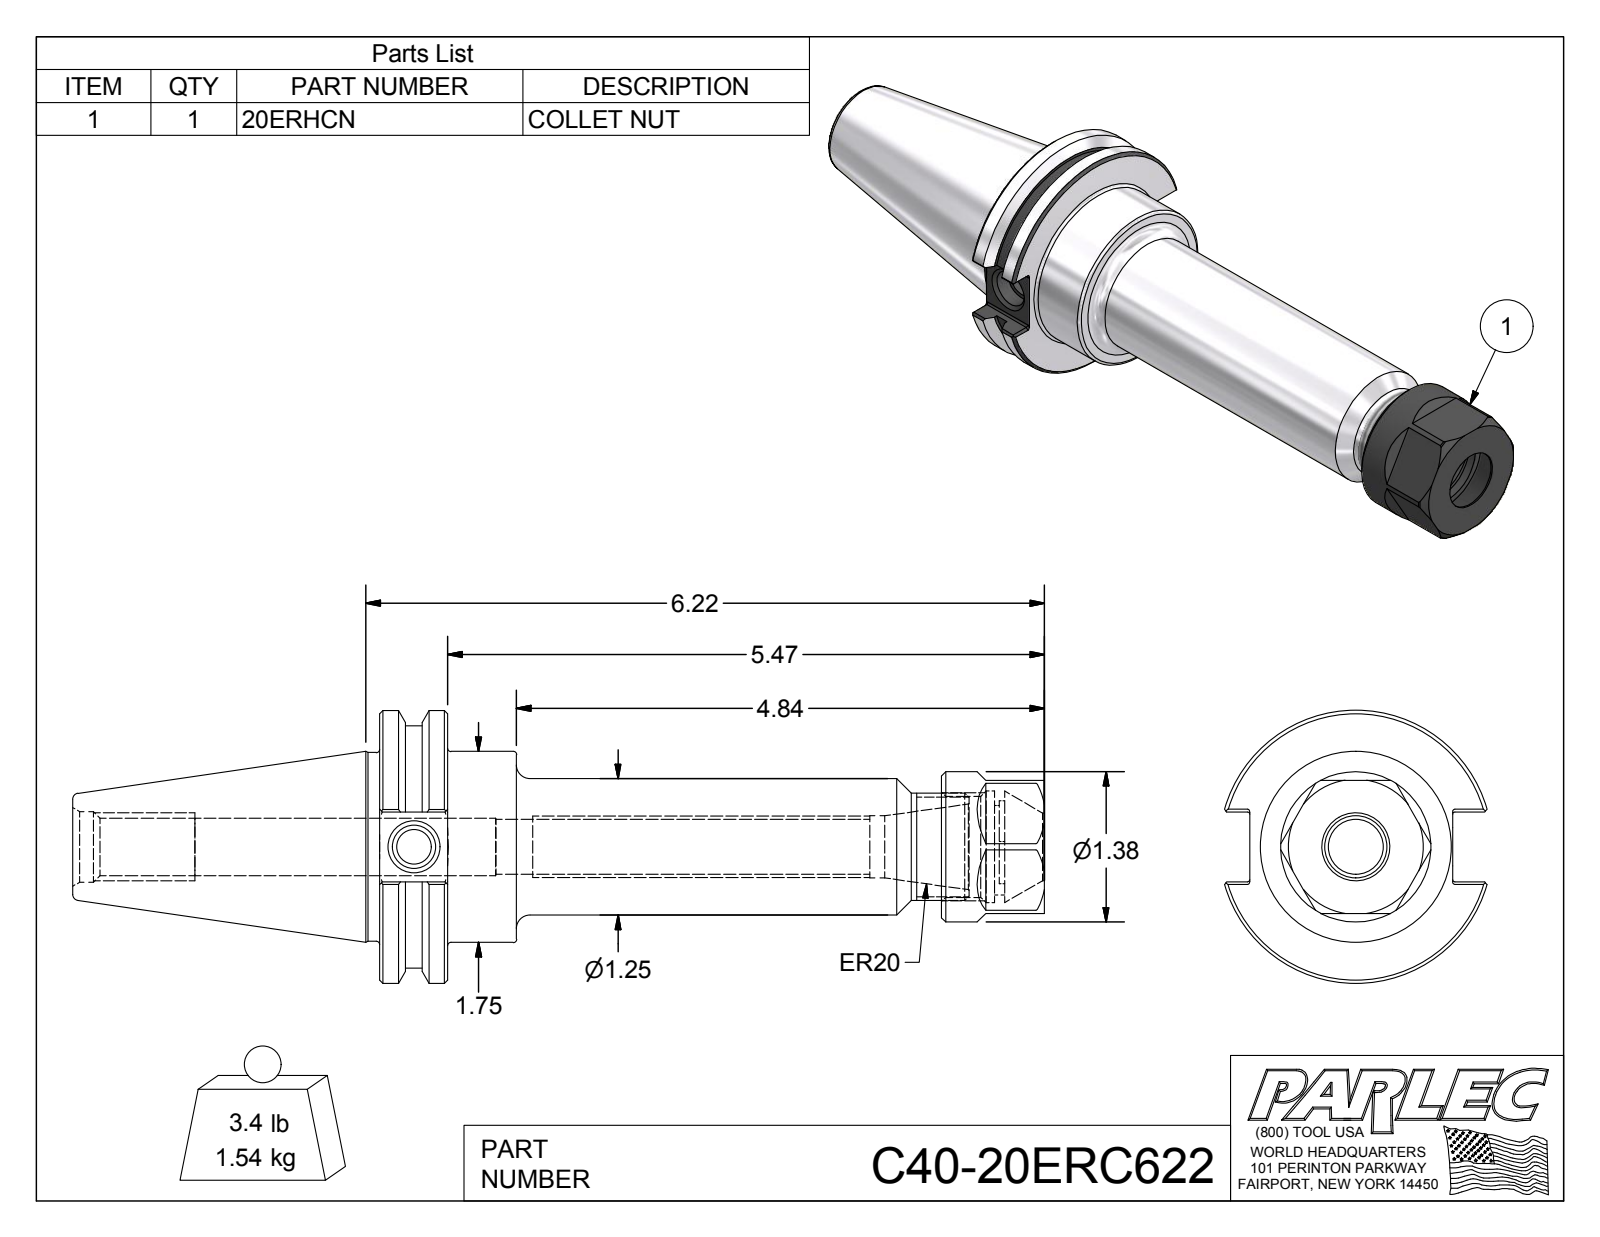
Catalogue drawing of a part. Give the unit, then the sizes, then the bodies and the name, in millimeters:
Units: millimetres
Overall size (bounding box): 226.25 × 63.5 × 61.05
Round holes (diameter × count): ⌀8 ×1, ⌀10.13 ×1, ⌀12.75 ×1, ⌀13.36 ×1, ⌀13.39 ×1, ⌀14.48 ×1, ⌀15.76 ×1, ⌀16.46 ×1, ⌀20.83 ×1, ⌀23.5 ×1, ⌀26 ×1
Round bosses / shafts (diameter × count): ⌀63.5 ×1, ⌀56.36 ×1, ⌀44.45 ×1, ⌀43.94 ×1, ⌀35 ×1, ⌀31.75 ×1, ⌀25 ×1
Partial cylindrical surfaces — rounded edges, fillets, slot ends (radius × count): R0.51 ×12, R10.75 ×1
Main face-to-face distances: 15.88, 154.82, 138.94, 31, 130.82, 114.94, 24, 31.88, 16, 98.94
Hole centre spacings: 0.95
Volume: 197 795 mm³ · Surface area: 43 077 mm²
Bodies: 2 solids, 126 faces (50 planar, 35 cylindrical, 41 other)
Part name (STEP PRODUCT): C40-20ER6-1; 20ERHCN; C40-20ERC622
STEP written by: Autodesk Inventor 2016 (AUTOMOTIVE_DESIGN)
